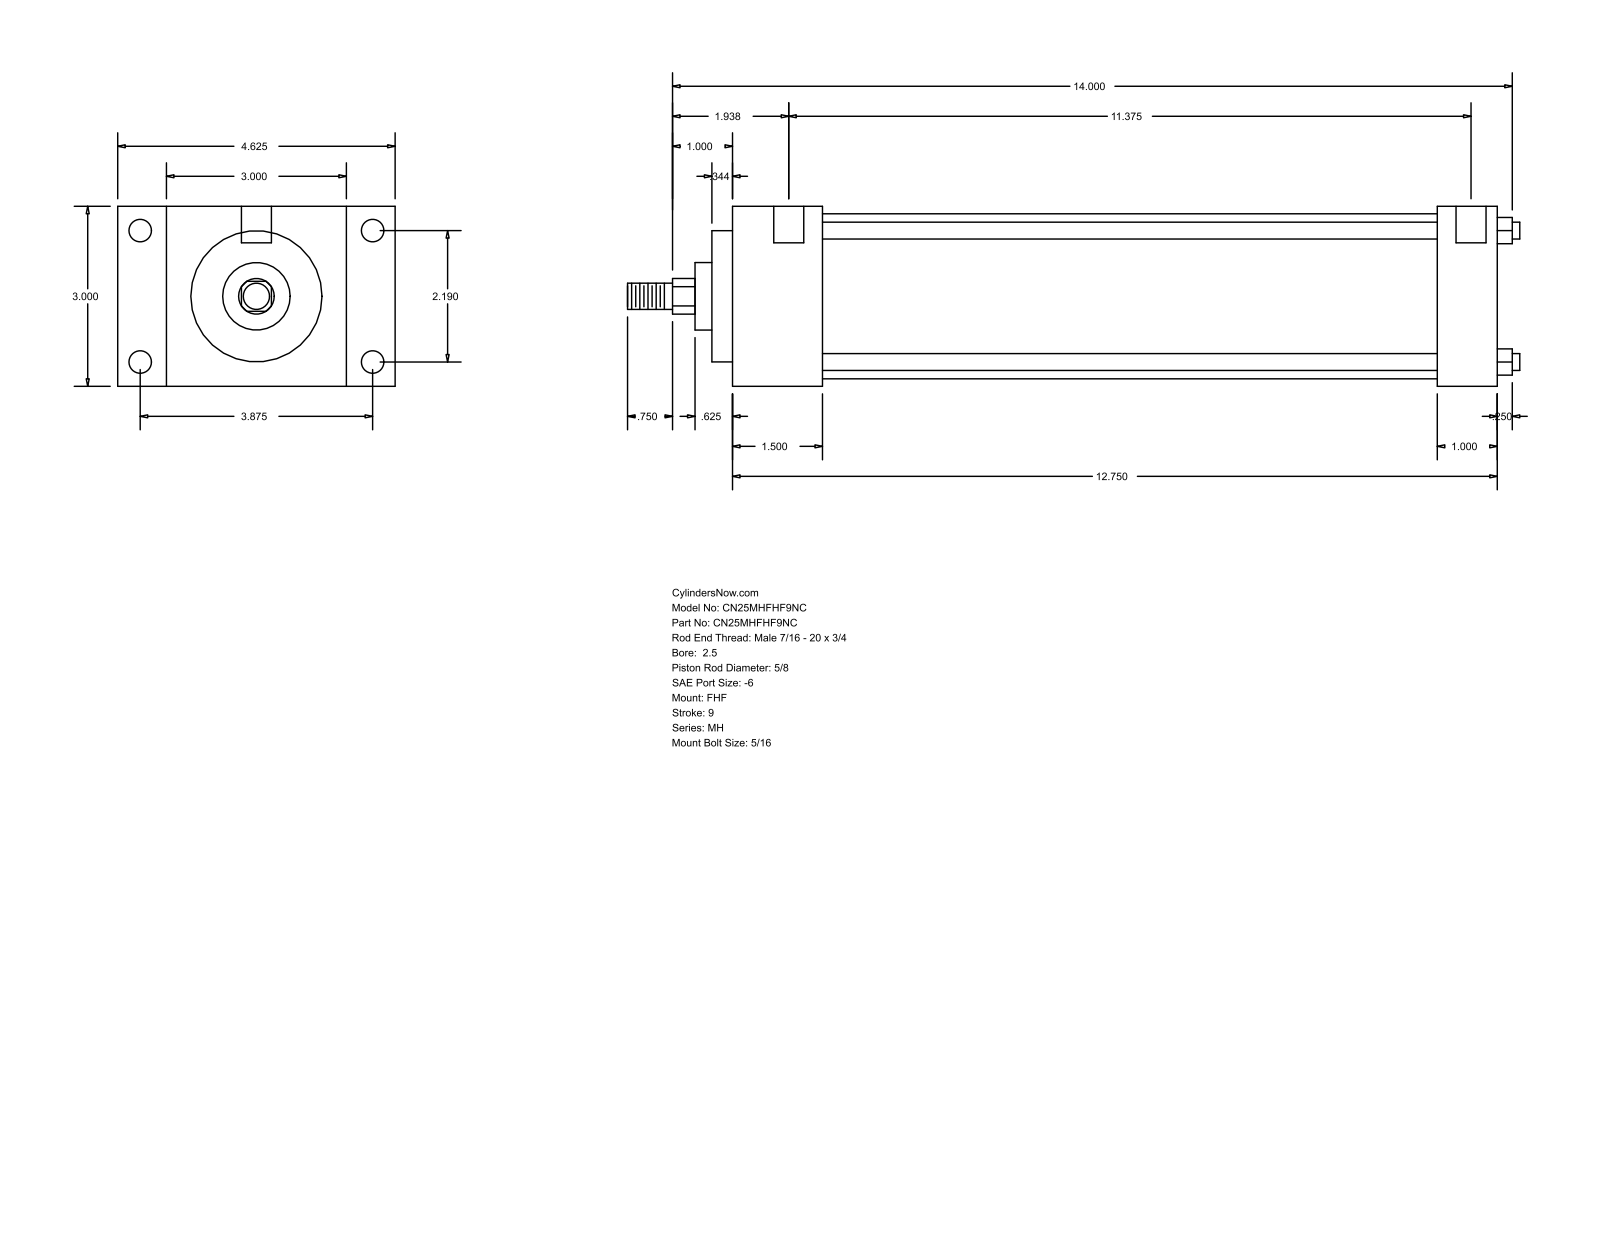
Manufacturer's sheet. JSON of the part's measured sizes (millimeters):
{"part_name": "MH_FHF__0250_0.625", "step_written_by": "GSSL Pune (CONFIG_CONTROL_DESIGN)", "units": "millimeters", "bodies": {"solids": 0, "faces": 90, "planar": 61, "cylindrical": 29, "other": 0}, "overall_size": [377.82, 117.47, 76.2], "round_holes": [[5.56, 4], [9.53, 4], [12.7, 2]], "round_bosses_or_shafts": [[7.14, 4], [69.85, 1], [55.55, 1], [28.57, 1], [15.88, 1], [11.11, 1]], "partial_cylinders_radius": [[7.54, 1]], "face_to_face_distances": [76.2, 323.85, 38.1, 285.75, 20.64, 96.84, 117.48, 25.4, 298.45, 260.35], "hole_center_spacings": [55.62, 98.42, 113.05, 296.86, 3.17, 4.76, 288.93, 292.1]}
